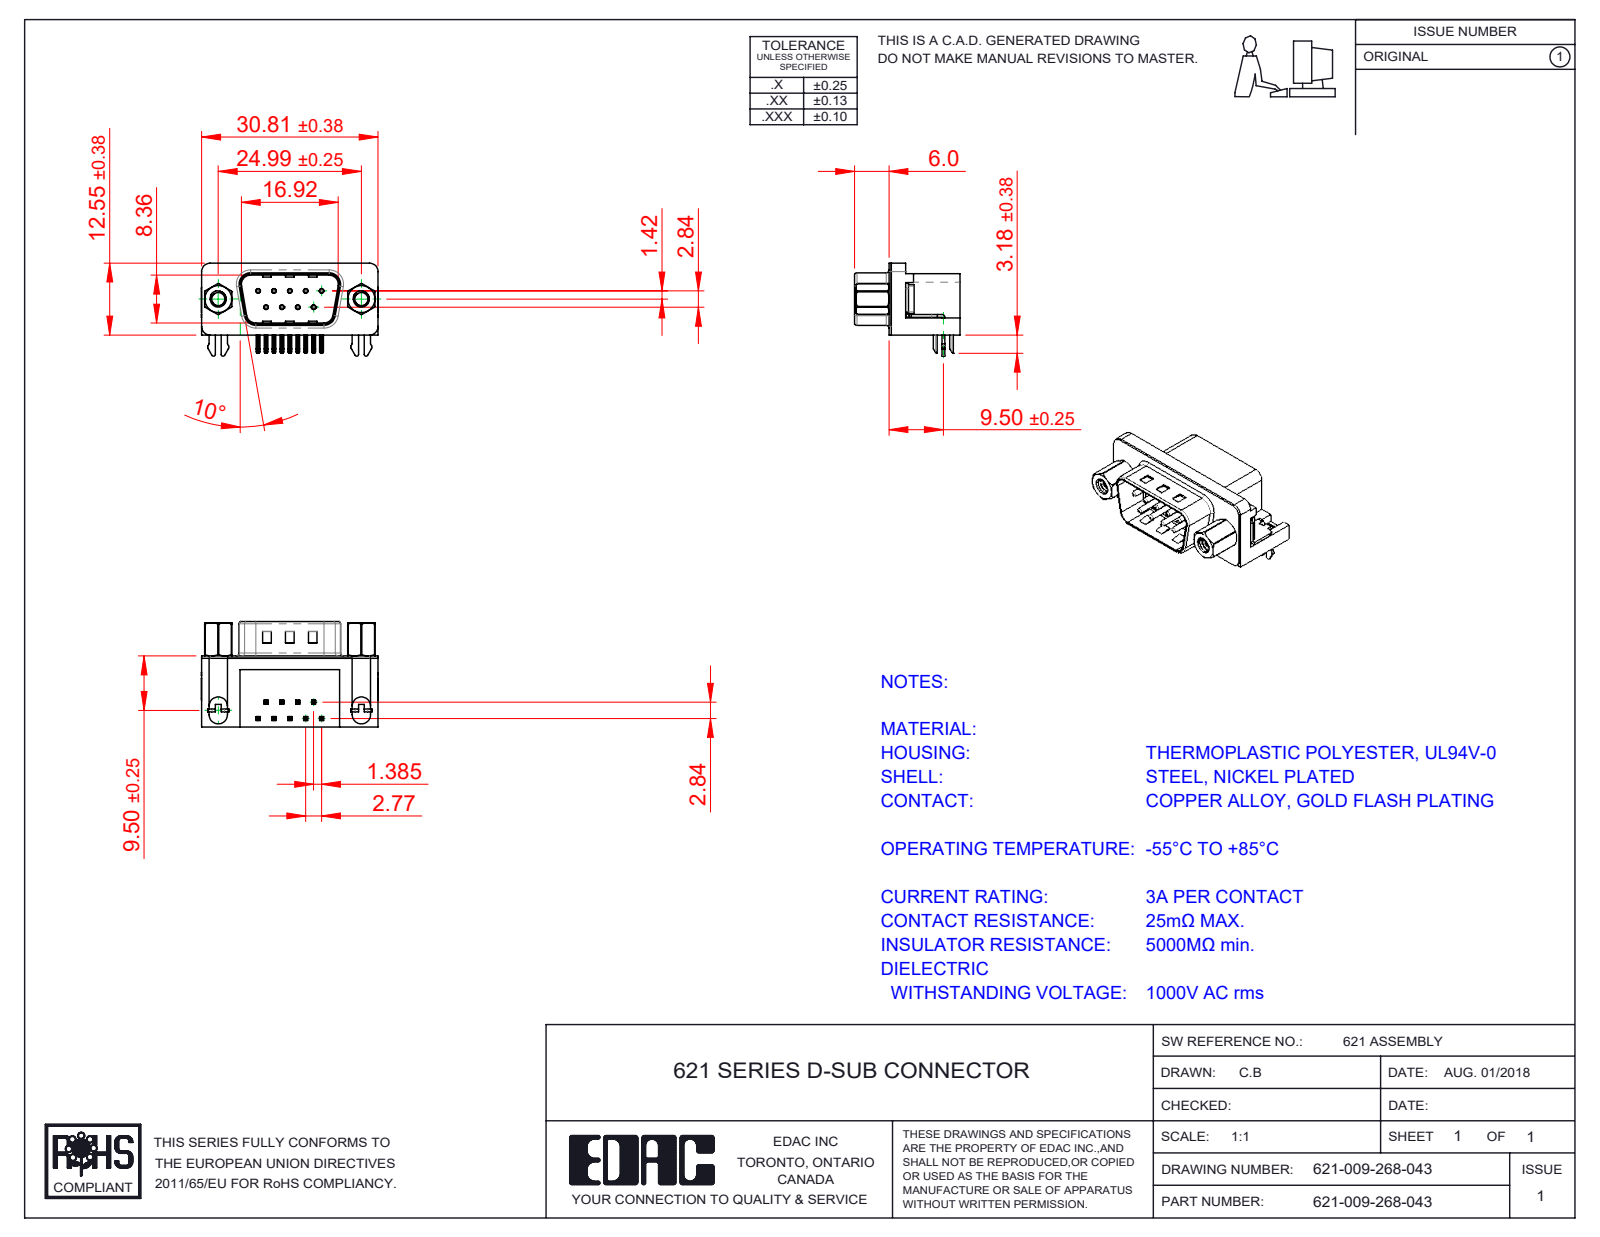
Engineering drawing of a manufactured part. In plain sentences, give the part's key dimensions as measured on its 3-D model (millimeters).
The part is named "621 Shell_9 Socket; 621 Contact Bottom; 621-009-268-043; 621 Contact Top (+4 more)". Its 3-D file was written by "SolidWorks 2016 (CONFIG_CONTROL_DESIGN)". It is 17 solids with 1237 faces: 637 planar, 393 cylindrical and 207 other. Overall it measures 30.89 by 18.4 by 16.25 millimeters. Its volume is 3 469 cubic millimeters and its surface area 4 978 square millimeters. Round holes: 9 of diameter 0.35, 9 of diameter 0.8, 2 of diameter 2, 2 of diameter 2.26, 2 of diameter 2.29, 2 of diameter 4, 2 of diameter 4.8, 2 of diameter 5. Round bosses or shafts: 9 of diameter 0.75, 2 of diameter 4.9, 2 of diameter 4.75, 2 of diameter 3.9, 2 of diameter 3, 2 of diameter 2.79. Partial cylindrical surfaces (rounded edges, fillets, slot ends): 48 of radius 0.25, 18 of radius 0.12, 16 of radius 1, 9 of radius 0.5, 8 of radius 1.5, 8 of radius 1.6, 4 of radius 0.9, 4 of radius 2. The main face-to-face distances are 0.4, 12, 12.4, 10.35, 9.5, 2.5, 2.9, 2.1, 0.35, 10.7. The hole center spacings are 3.16, 2.77, 5.54, 5.03, 5.04, 8.31, 7.48, 7.49.
